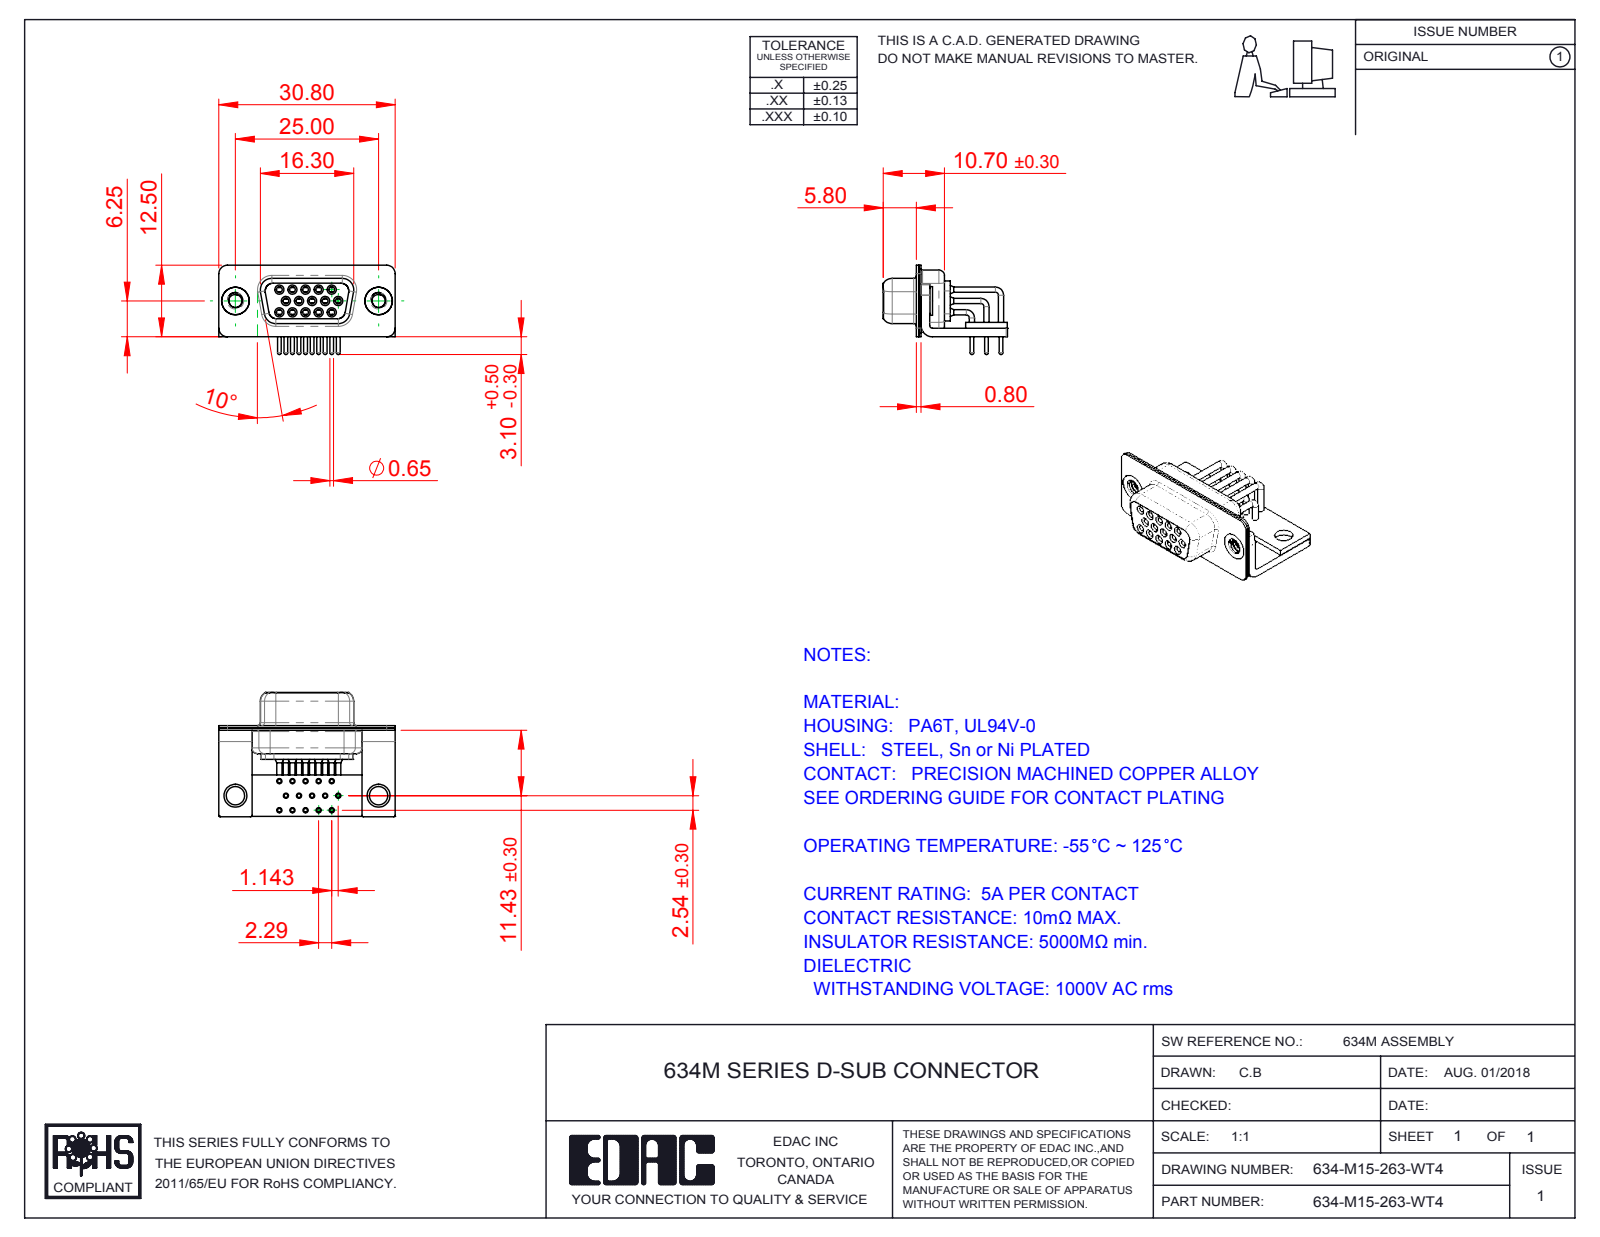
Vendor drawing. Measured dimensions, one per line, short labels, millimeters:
name: 634M 4-40 Threaded Rivet_Stabilizer; 634M Contact Row 3; 634M Contact Row 2; 634M Contact Row 1 (+6 more)
written by: SolidWorks 2016 (CONFIG_CONTROL_DESIGN)
unit: mm
bodies: 23 solids, 1154 faces (318 planar, 534 cylindrical, 302 other)
size: 30.8 × 21.7 × 15.6
volume: 2 216 mm³; area: 6 817 mm²
holes: 15× ⌀0.9, 15× ⌀1, 15× ⌀1.1, 15× ⌀1.7, 15× ⌀1.8, 15× ⌀2, 2× ⌀2.26, 2× ⌀3.2, 2× ⌀4, 2× ⌀4.8
bosses: 15× ⌀1.6, 15× ⌀1.5, 15× ⌀0.9, 15× ⌀0.65, 2× ⌀5, 2× ⌀4.9, 1× ⌀2
rounds: 16× R0.25, 16× R1.5, 13× R2, 8× R1.35, 8× R1.6, 5× R0.5, 4× R0.6, 4× R0.65
face distances: 0.4, 0.8, 1.5, 1, 2.3, 1.9, 9.35, 2.5, 1.45, 0.85
hole spacings: 2.29, 2.28, 4.57, 3.96, 4.27, 2.78, 6.05, 6.86
